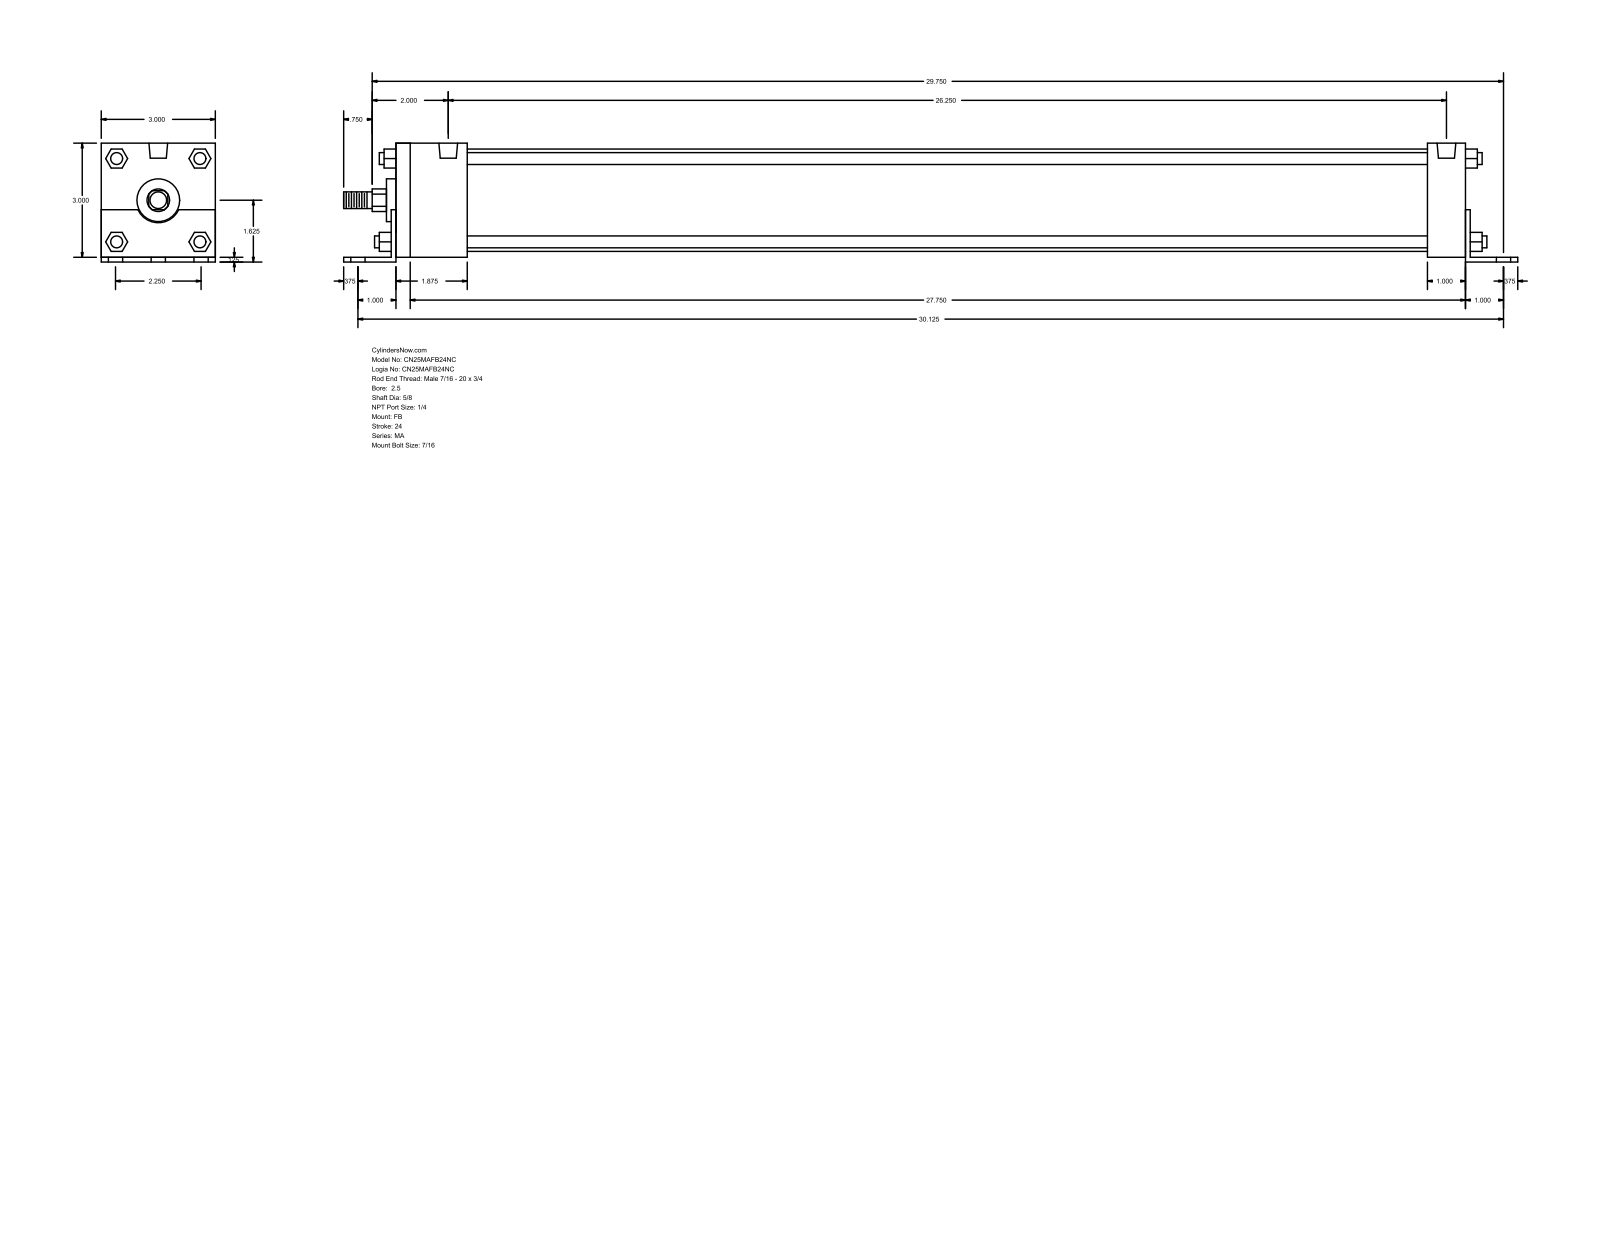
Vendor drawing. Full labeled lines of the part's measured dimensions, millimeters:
Part name (STEP PRODUCT): MA_FB__0250_0.625
STEP written by: GSSL Pune (CONFIG_CONTROL_DESIGN)
Units: millimetres
Bodies: 0 solids, 140 faces (105 planar, 35 cylindrical, 0 other)
Overall size (bounding box): 784.23 × 79.38 × 76.2
Round holes (diameter × count): ⌀11.11 ×6, ⌀7.94 ×4, ⌀12.49 ×2
Round bosses / shafts (diameter × count): ⌀7.94 ×4, ⌀68.33 ×1, ⌀28.57 ×1, ⌀15.88 ×1, ⌀11.11 ×1
Partial cylindrical surfaces — rounded edges, fillets, slot ends (radius × count): R7.54 ×1, R15.05 ×1
Main face-to-face distances: 76.2, 3.17, 79.37, 714.37, 720.72, 3.18, 717.54, 47.62, 25.4, 717.55
Hole centre spacings: 28.57, 765.71, 765.18, 47.62, 57.14, 66.75, 666.75, 705.43
